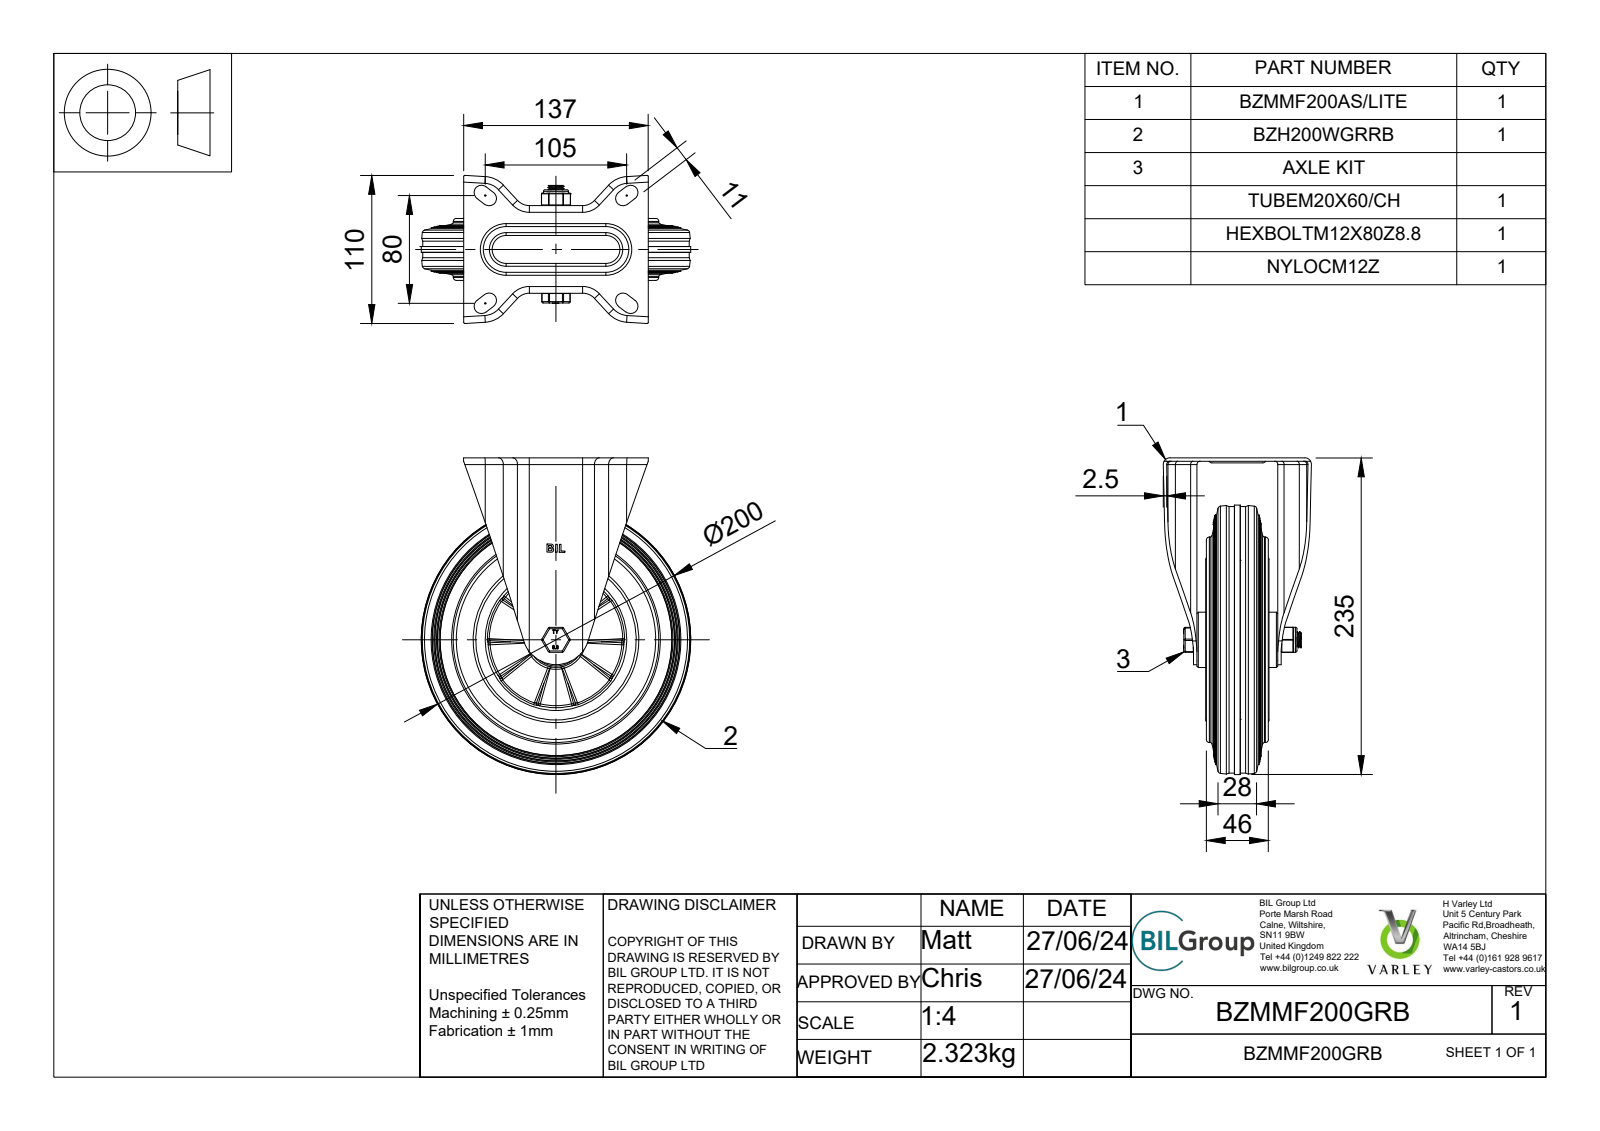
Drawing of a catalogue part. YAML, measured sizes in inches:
part_name: "BZMMF200GRB v3; BZMMF200AS/LITE v4; ZINC PLATED, PRESSED STEELM BRACKET; BZH200WGRRB v1 (+7 more)"
step_written_by: "Autodesk Translation Framework v13.14.0.145 (AUTOMOTIVE_DESIGN)"
units: inches
bodies: {solids: 17, faces: 846, planar: 223, cylindrical: 196, other: 427}
overall_size: [9.252, 7.874, 4.326]
volume: 67.55
surface_area: 444.2
round_holes:
  - {diameter: 0.472, count: 1}
  - {diameter: 0.482, count: 1}
  - {diameter: 0.492, count: 1}
  - {diameter: 0.551, count: 1}
  - {diameter: 0.787, count: 1}
  - {diameter: 1.378, count: 1}
  - {diameter: 3.976, count: 1}
  - {diameter: 4.646, count: 1}
round_bosses_or_shafts:
  - {diameter: 0.295, count: 8}
  - {diameter: 7.788, count: 1}
  - {diameter: 6.004, count: 1}
  - {diameter: 4.843, count: 1}
  - {diameter: 1.614, count: 1}
  - {diameter: 1.374, count: 1}
  - {diameter: 1.339, count: 1}
  - {diameter: 0.783, count: 1}
partial_cylinders:
  - {radius: 0.02, count: 18}
  - {radius: 0.098, count: 18}
  - {radius: 0.039, count: 12}
  - {radius: 0.197, count: 10}
  - {radius: 0.217, count: 8}
  - {radius: 0.472, count: 4}
  - {radius: 0.571, count: 4}
  - {radius: 0.689, count: 4}
face_to_face_distances: [0.098, 2.461, 0.354, 2.106, 2.362, 0.256, 0.197, 2.028, 1.909, 0.453]
